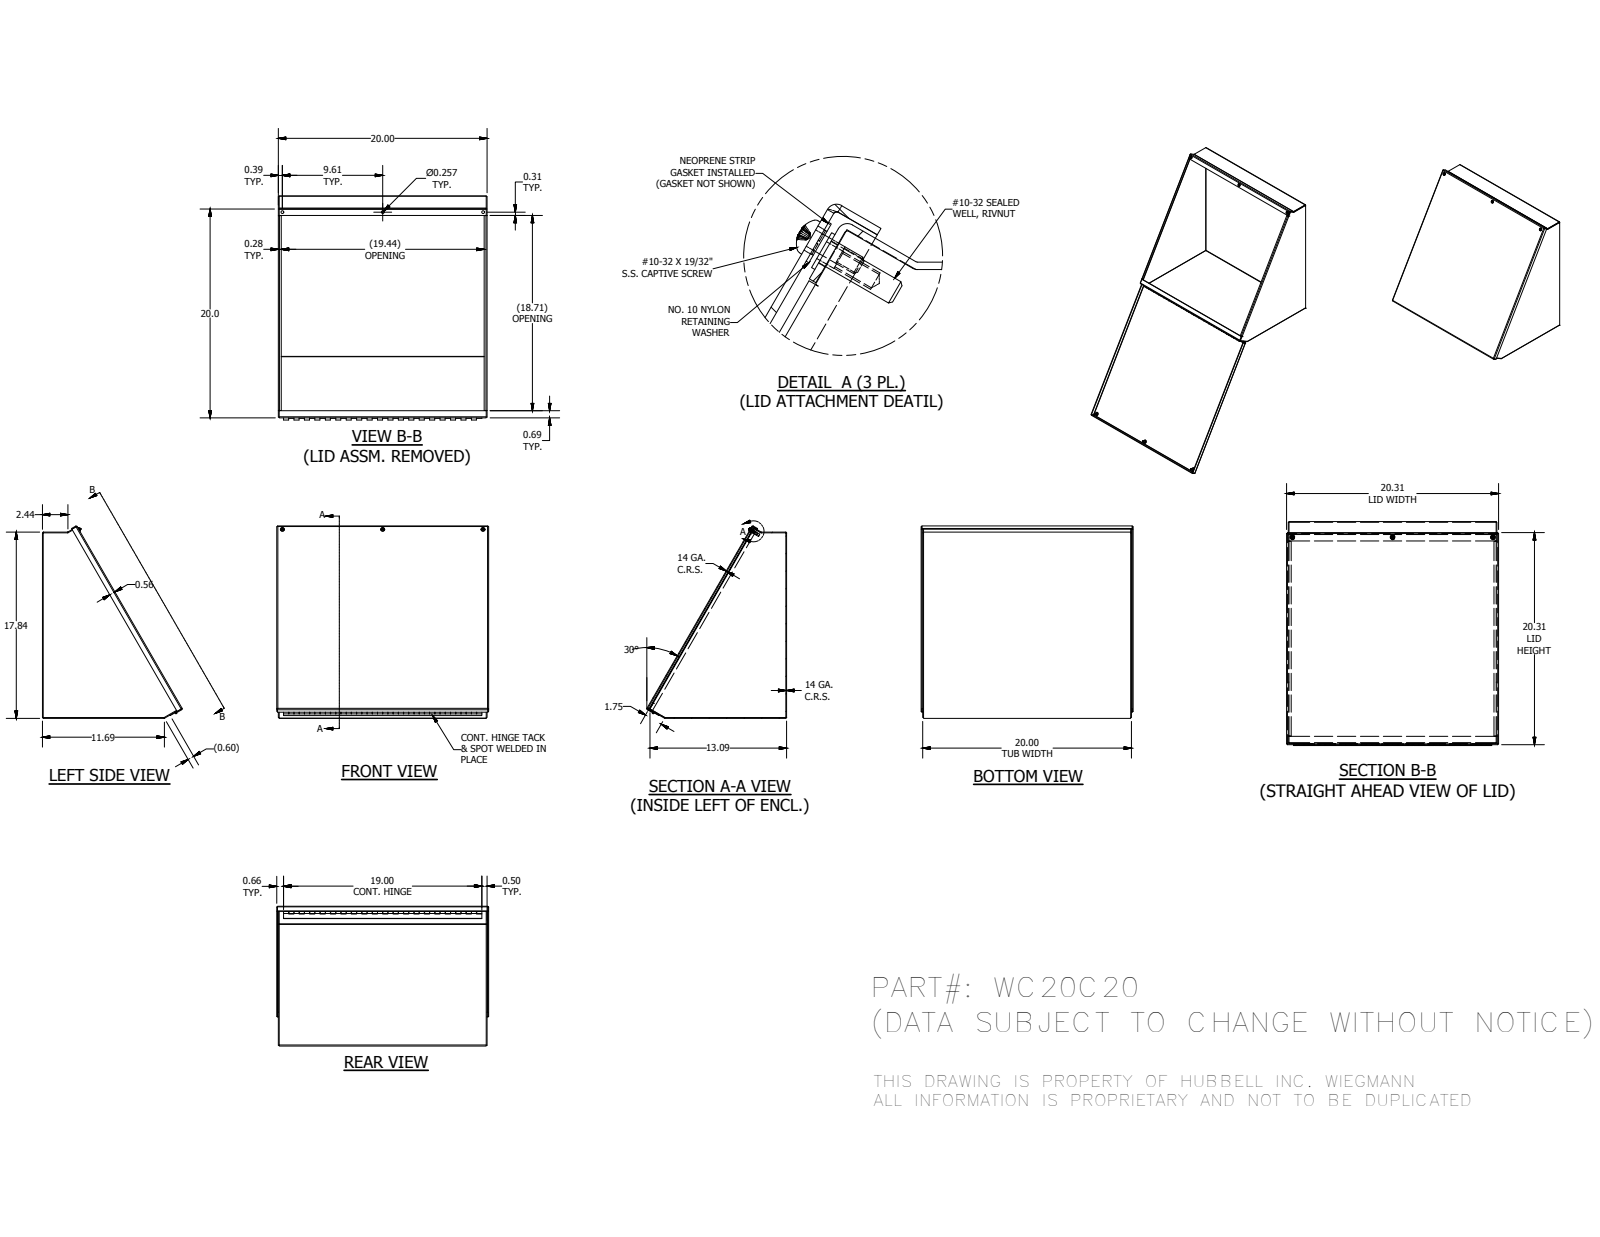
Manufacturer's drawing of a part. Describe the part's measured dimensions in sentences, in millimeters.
The part is named "WC20C20BTB; WC20C20LID; WC20CLS; WC20CRS (+8 more)". Its 3-D file was written by "Autodesk Inventor 2014 (AUTOMOTIVE_DESIGN)". It is 16 solids with 557 faces: 340 planar, 143 cylindrical and 74 other. Overall it measures 515.94 by 468.05 by 340.23 millimeters. Its volume is 1 796 000 cubic millimeters and its surface area 1 946 000 square millimeters. Round holes: 3 of diameter 3.96, 3 of diameter 4.98, 3 of diameter 6.53, 3 of diameter 7.06, 3 of diameter 7.14, 1 of diameter 2.96. Round bosses or shafts: 3 of diameter 11.51, 3 of diameter 10.31, 3 of diameter 9.47, 3 of diameter 6.3, 3 of diameter 4.83, 1 of diameter 5.08, 1 of diameter 2.54. Partial cylindrical surfaces (rounded edges, fillets, slot ends): 12 of radius 0.79, 12 of radius 2.67, 3 of radius 2.27. The main face-to-face distances are 1.88, 506.12, 504.24, 508, 451.35, 449.47, 453.23, 2.94, 3.97, 510.09. The hole center spacings are 244.17, 488.34, 1.31.
